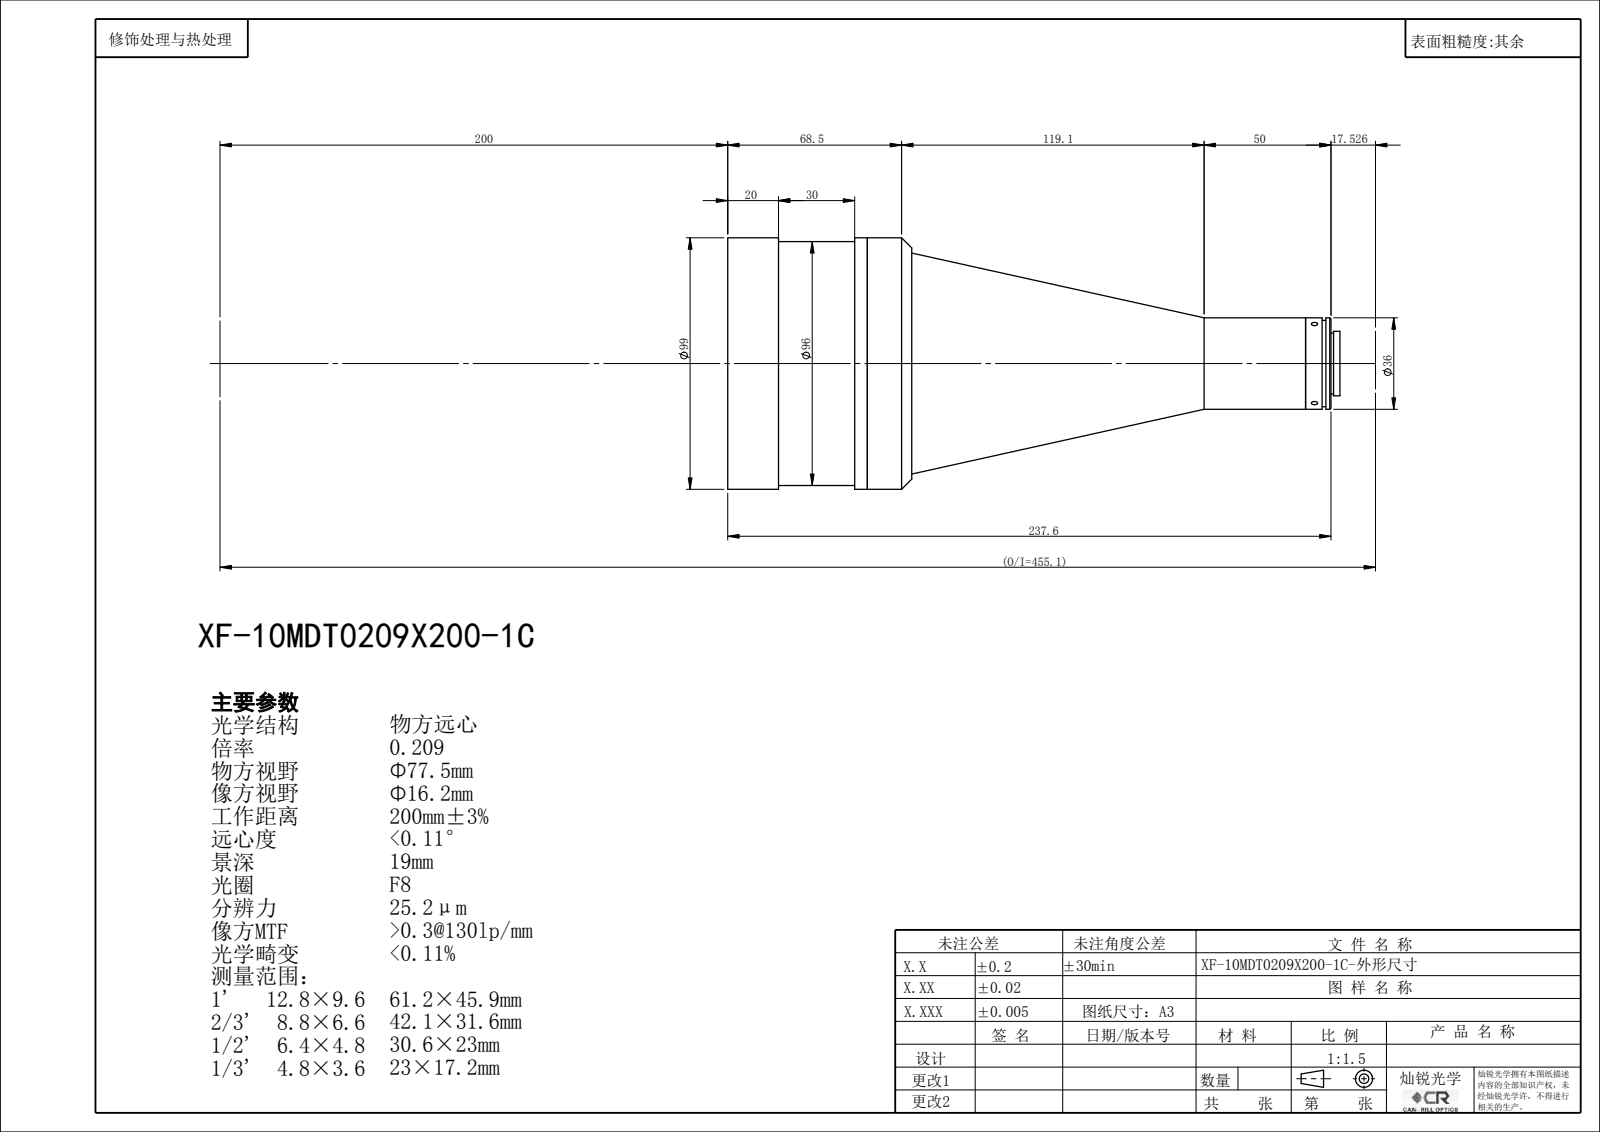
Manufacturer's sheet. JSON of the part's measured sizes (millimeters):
{"part_name": "XF-5MDT0209X200-1C", "step_written_by": "SolidWorks 2014 (CONFIG_CONTROL_DESIGN)", "units": "millimeters", "bodies": {"solids": 0, "faces": 85, "planar": 33, "cylindrical": 38, "other": 14}, "overall_size": [241.14, 99, 99], "round_holes": [[2.5, 3], [21.4, 1], [22, 1], [26, 1], [85, 1], [92, 1]], "round_bosses_or_shafts": [[99, 1], [96, 1], [87, 1], [36, 1], [34, 1], [25.4, 1], [24, 1]], "face_to_face_distances": [55, 5, 9.53, 45.47, 72.5, 62.97, 17.5, 237.64, 228.11, 182.64]}
